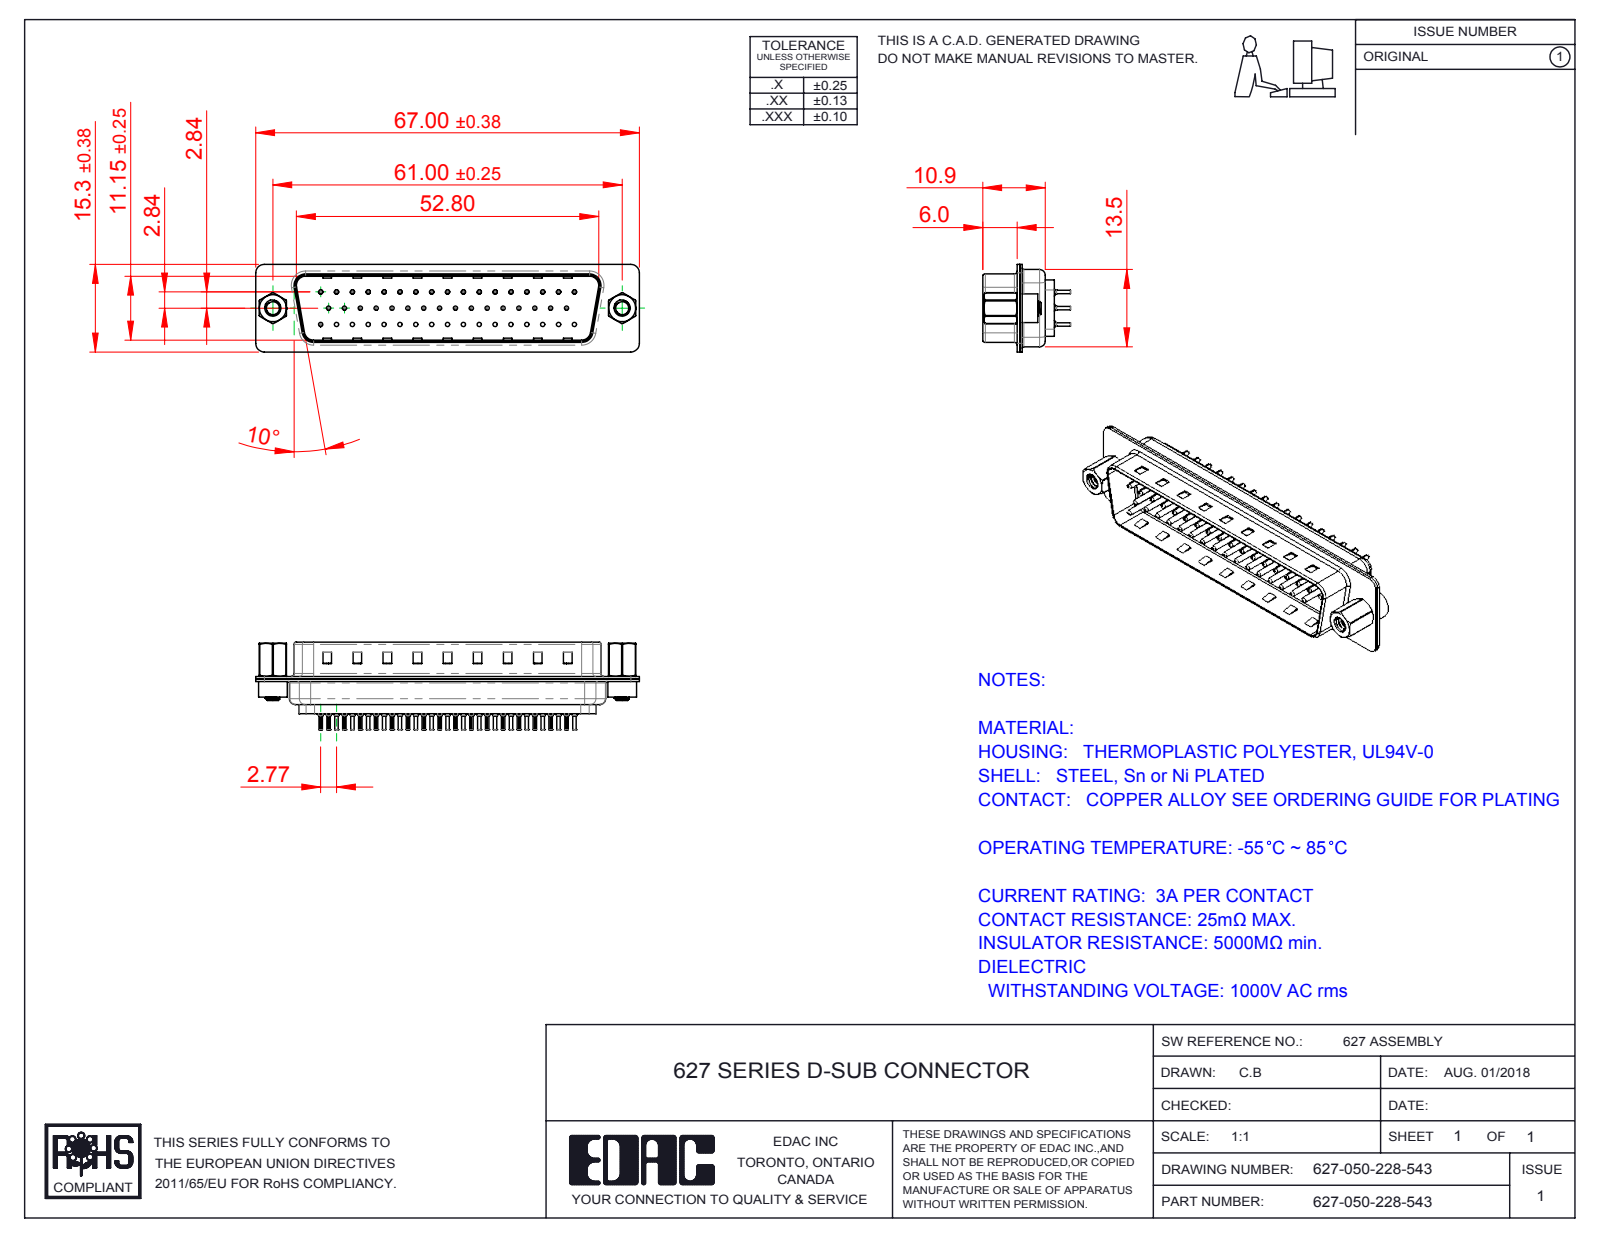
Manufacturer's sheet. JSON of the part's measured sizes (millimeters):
{"part_name": "627 4-40 Hex Standoff; 627 Housing_50 LP; 627 Contact Row 2_28L; 627-050-228-543 (+5 more)", "step_written_by": "SolidWorks 2016 (CONFIG_CONTROL_DESIGN)", "units": "millimeters", "bodies": {"solids": 41, "faces": 3998, "planar": 1073, "cylindrical": 1567, "other": 1358}, "overall_size": [67, 15.3, 15.3], "volume_mm3": 4492, "surface_area_mm2": 11455, "round_holes": [[1.6, 50], [0.2, 34], [0.35, 34], [1.1, 34], [0.75, 16], [2, 16], [2.26, 2], [2.29, 2], [4, 2], [4.8, 2]], "round_bosses_or_shafts": [[2, 34], [1.5, 34], [0.75, 34], [0.6, 34], [5, 2], [4.9, 2], [2.79, 2]], "partial_cylinders_radius": [[0.1, 68], [1.5, 16], [2, 12], [0.5, 8], [1.6, 8], [0.25, 4], [0.6, 4], [0.65, 4]], "face_to_face_distances": [0.4, 0.45, 11.55, 0.9, 6.05, 6.5, 12.33, 0.78, 0.77, 12.32], "hole_center_spacings": [3.16, 2.77, 5.54, 8.31, 11.08, 13.85, 16.62, 5.03]}
